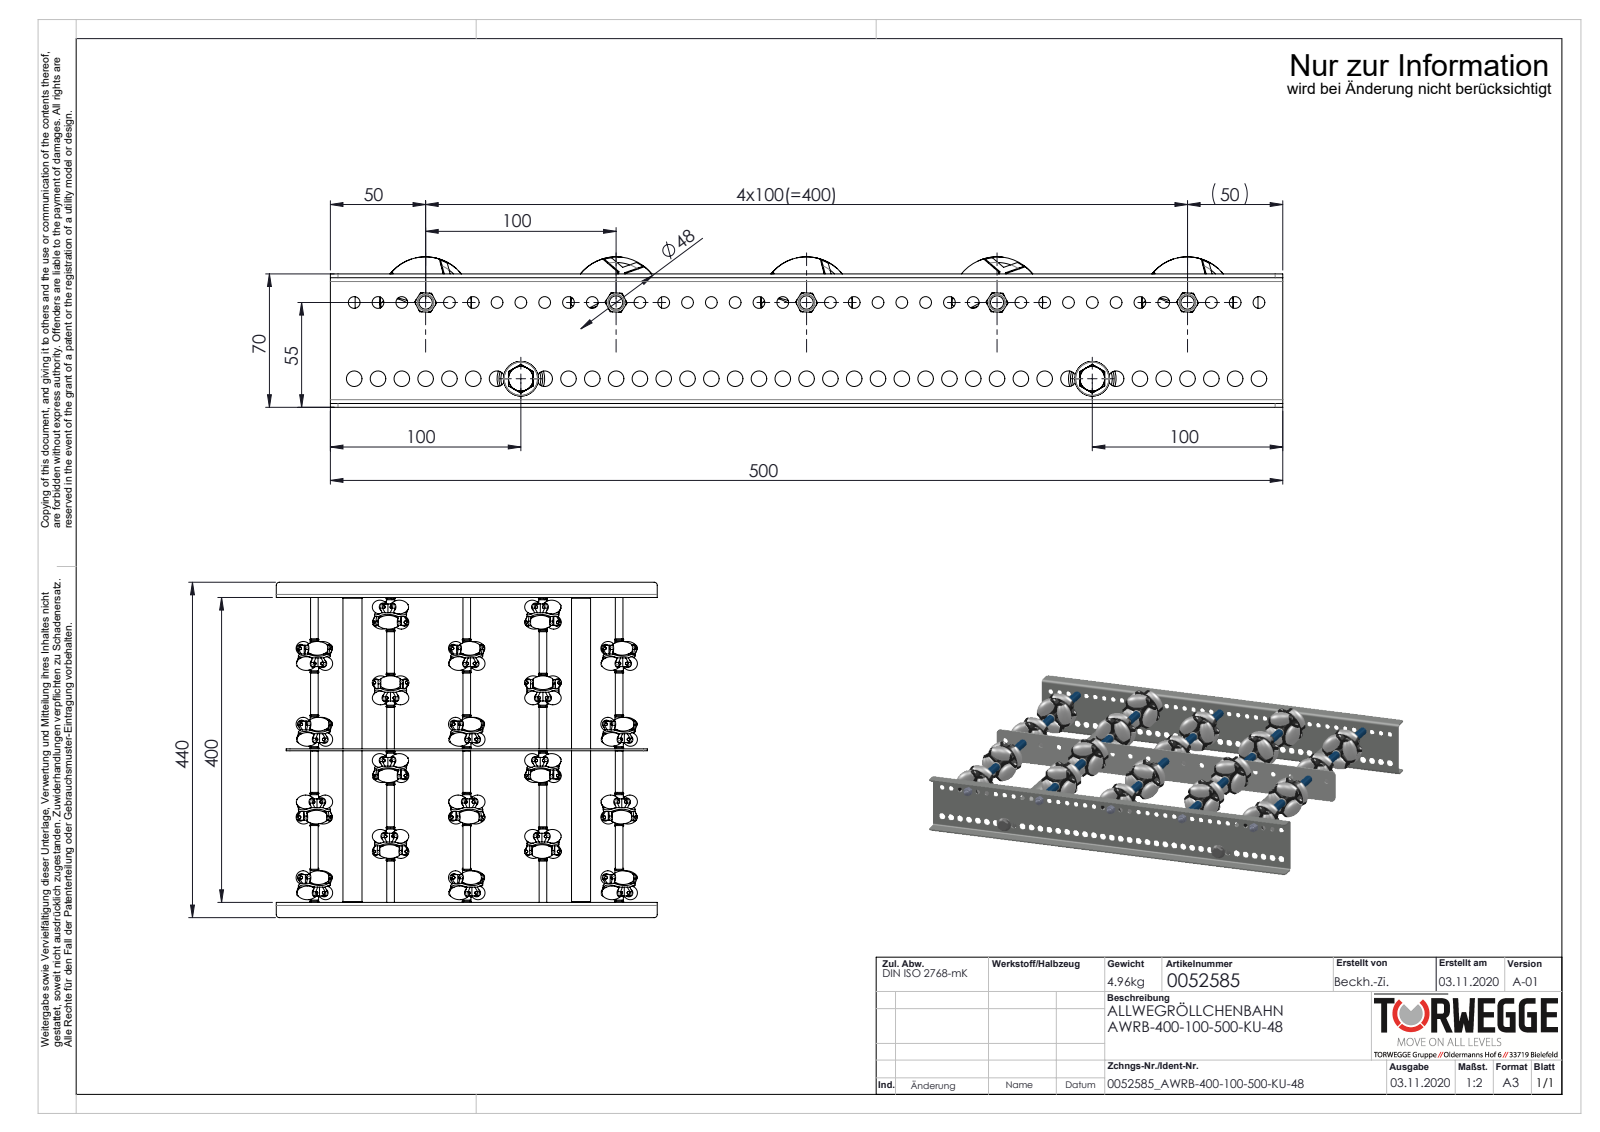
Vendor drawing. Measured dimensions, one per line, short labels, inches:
name: Traversen_KFG_L400; Profil-RB-20x70x20x2_S100208_U-PROFIL-20-70-20-2-RB-L=500; S100994_Sperrzahnschraube_M08x16-8.8-A2K; 0052585 (+8 more)
written by: SolidWorks 2020 (AUTOMOTIVE_DESIGN)
unit: in
bodies: 348 solids, 6410 faces (2176 planar, 2540 cylindrical, 1694 other)
size: 19.685 × 17.323 × 3.11
volume: 82.2 in³; area: 1 521 in²
holes: 120× ⌀0.146, 120× ⌀0.165, 39× ⌀0.244, 39× ⌀0.323, 19× ⌀0.256, 5× ⌀0.194, 5× ⌀0.331, 2× ⌀0.268, 2× ⌀0.827
bosses: 120× ⌀0.157, 98× ⌀0.146, 7× ⌀0.315, 5× ⌀1.654, 5× ⌀0.433, 5× ⌀0.394, 5× ⌀0.276, 5× ⌀0.236
rounds: 8× R0.157, 5× R0.927, 4× R0.079, 4× R0.197
face distances: 0.079, 15.827, 2.677, 15.748, 15.906, 0.581, 7.898, 7.819, 7.929, 8.008
hole spacings: 1.42, 1.419, 0.492, 0.984, 1.476, 1.969, 2.461, 2.953
